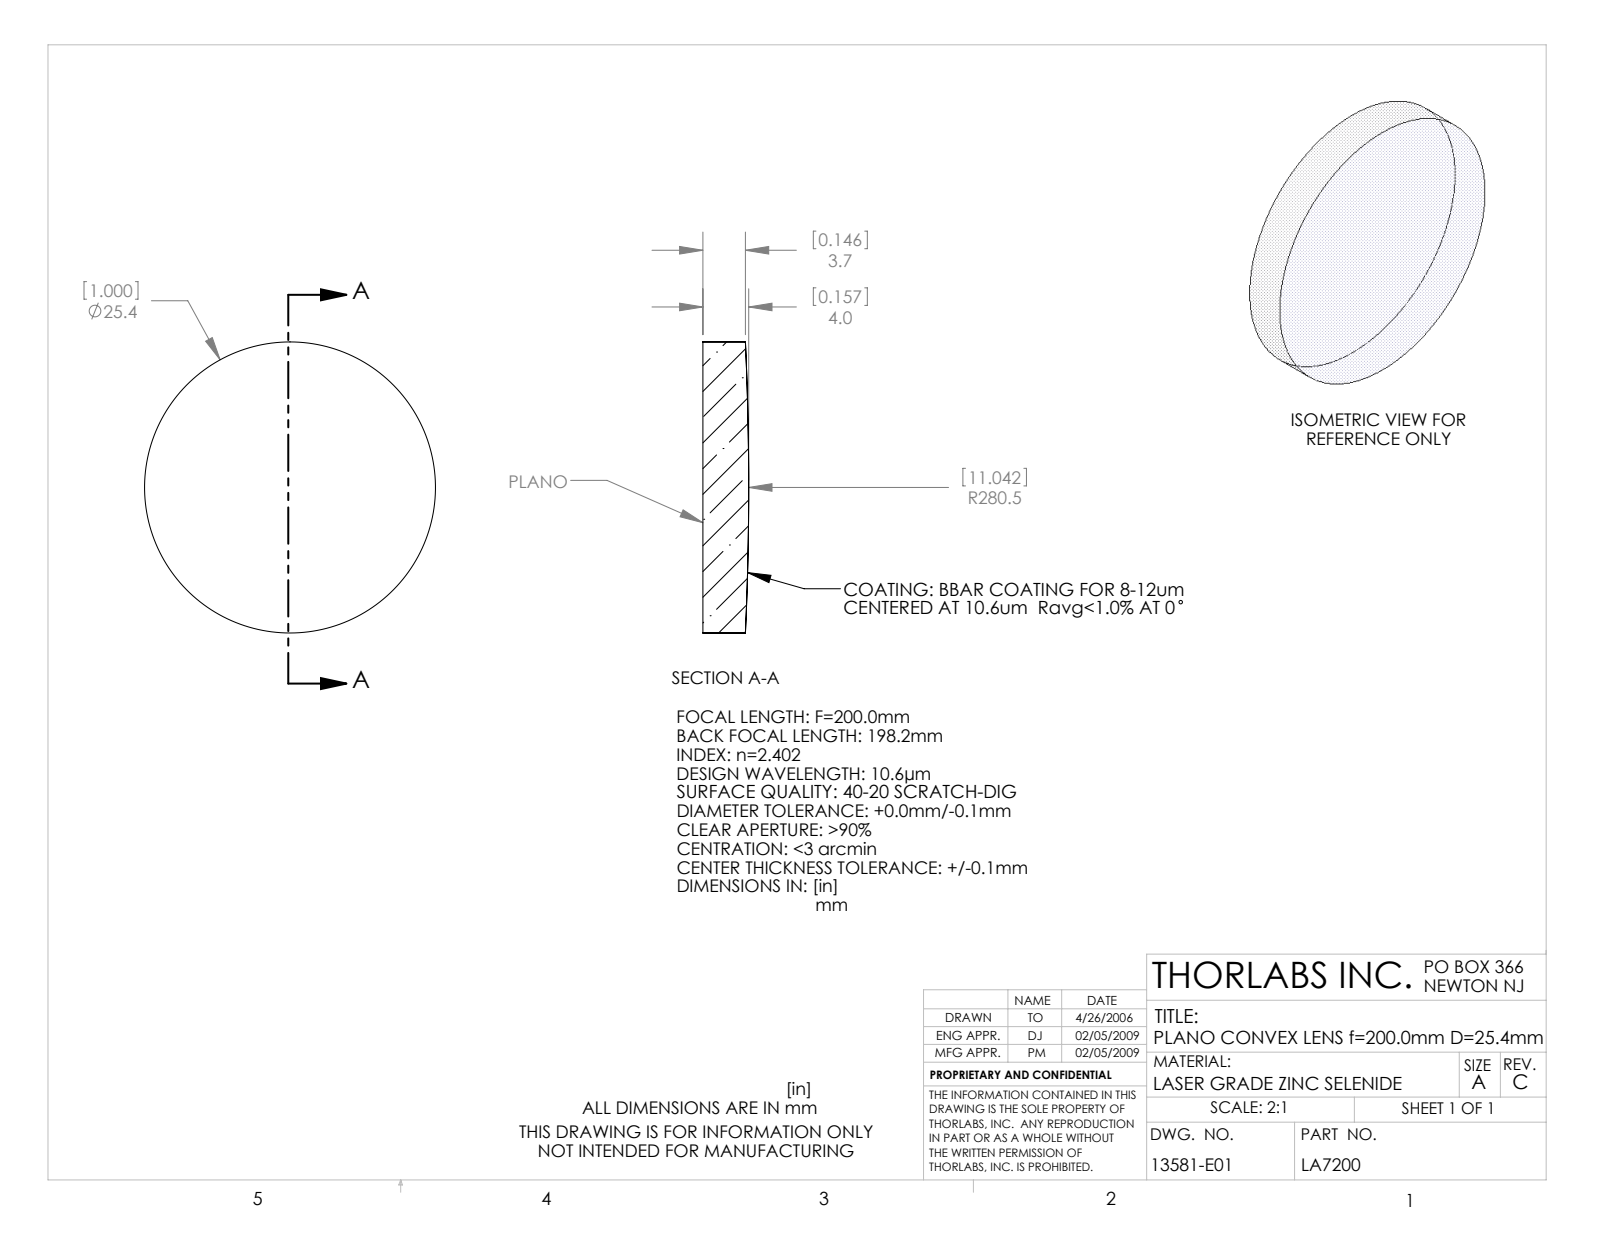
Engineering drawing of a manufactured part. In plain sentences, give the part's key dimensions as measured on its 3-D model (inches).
The part is named "13581-E0W". Its 3-D file was written by "SolidWorks 2007 (AUTOMOTIVE_DESIGN)". It is 0 solids with 5 faces: 1 planar, 2 cylindrical and 2 other. Overall it measures 1 by 1 by 0.157 inches. Round bosses or shafts: 1 of diameter 1.
